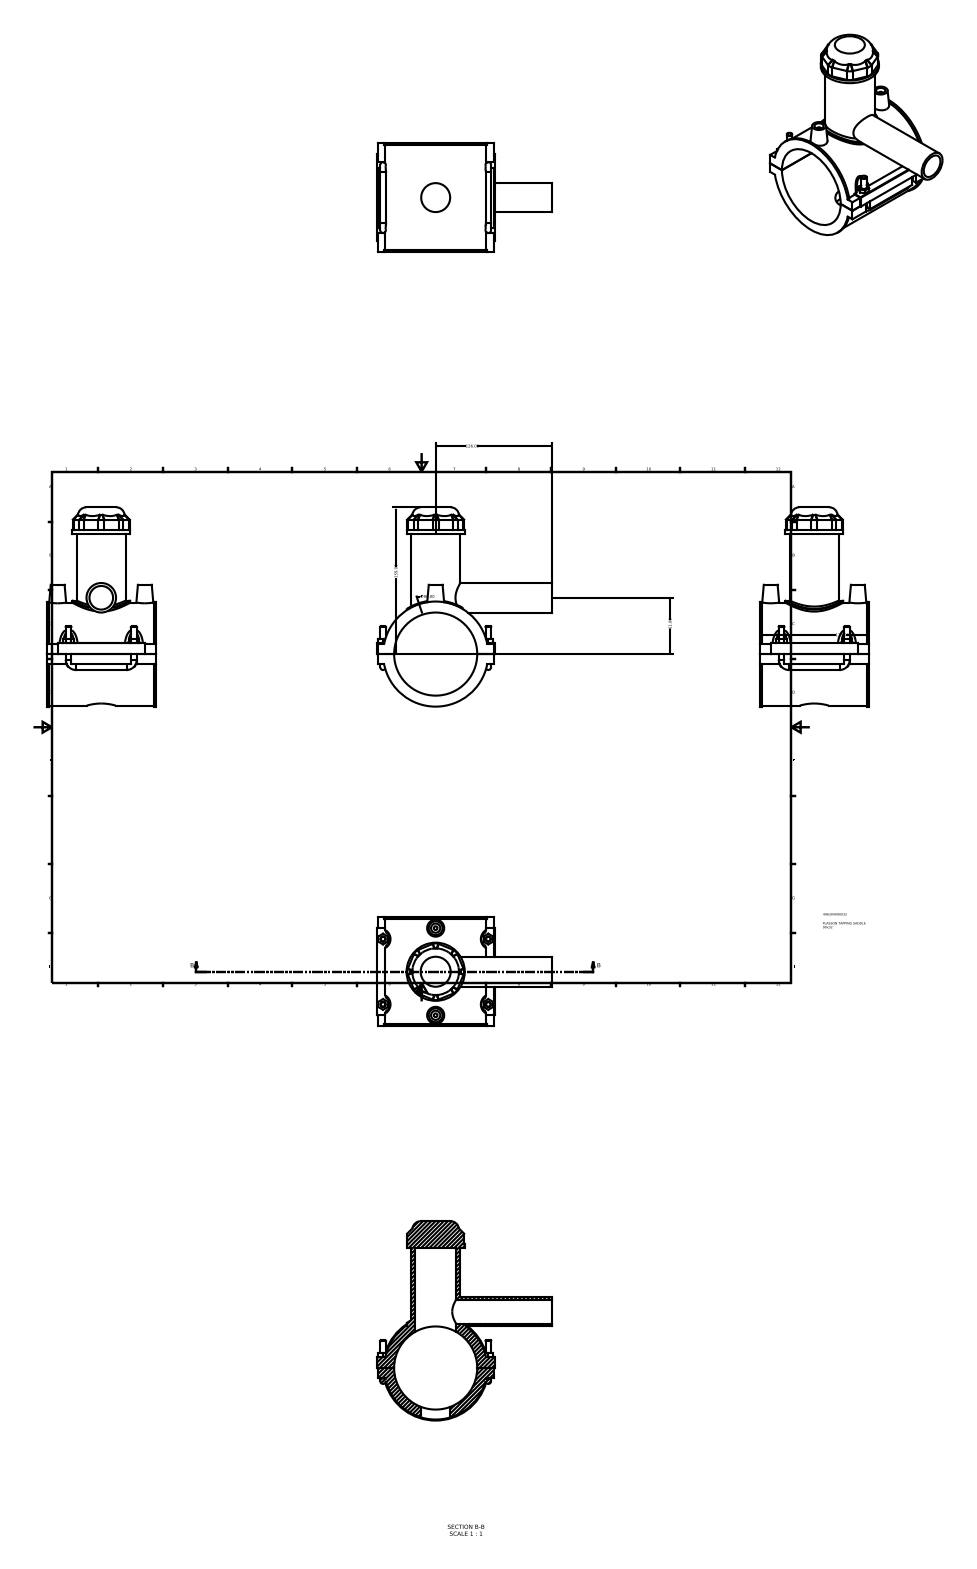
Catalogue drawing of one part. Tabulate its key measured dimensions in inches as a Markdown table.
| quantity | value |
| --- | --- |
| part name | 496304090032 |
| STEP written by | Autodesk Inventor 2015 (AUTOMOTIVE_DESIGN) |
| units | inches |
| bodies | 1 solid, 224 faces (125 planar, 55 cylindrical, 44 other) |
| overall size | 8.501 × 7.48 × 4.646 |
| volume | 35.91 in³ |
| surface area | 236 in² |
| round holes (diameter × count) | 0.394 × 2, 1.008 × 1, 1.235 × 1, 1.736 × 1, 3.543 × 1 |
| round bosses / shafts (diameter × count) | 0.236 × 6, 0.157 × 2, 4.481 × 1, 4.394 × 1, 2.48 × 1, 2.108 × 1, 1.26 × 1 |
| partial cylindrical surfaces (radius × count) | 0.354 × 8, 0.118 × 4, 0.295 × 4, 0.02 × 1, 2.285 × 1 |
| main face-to-face distances | 4.646, 0.039, 5.14, 5.136, 5, 0.441, 0.445, 5.581, 0.925, 0.484 |
| hole center spacings | 1.858, 3.717 |
